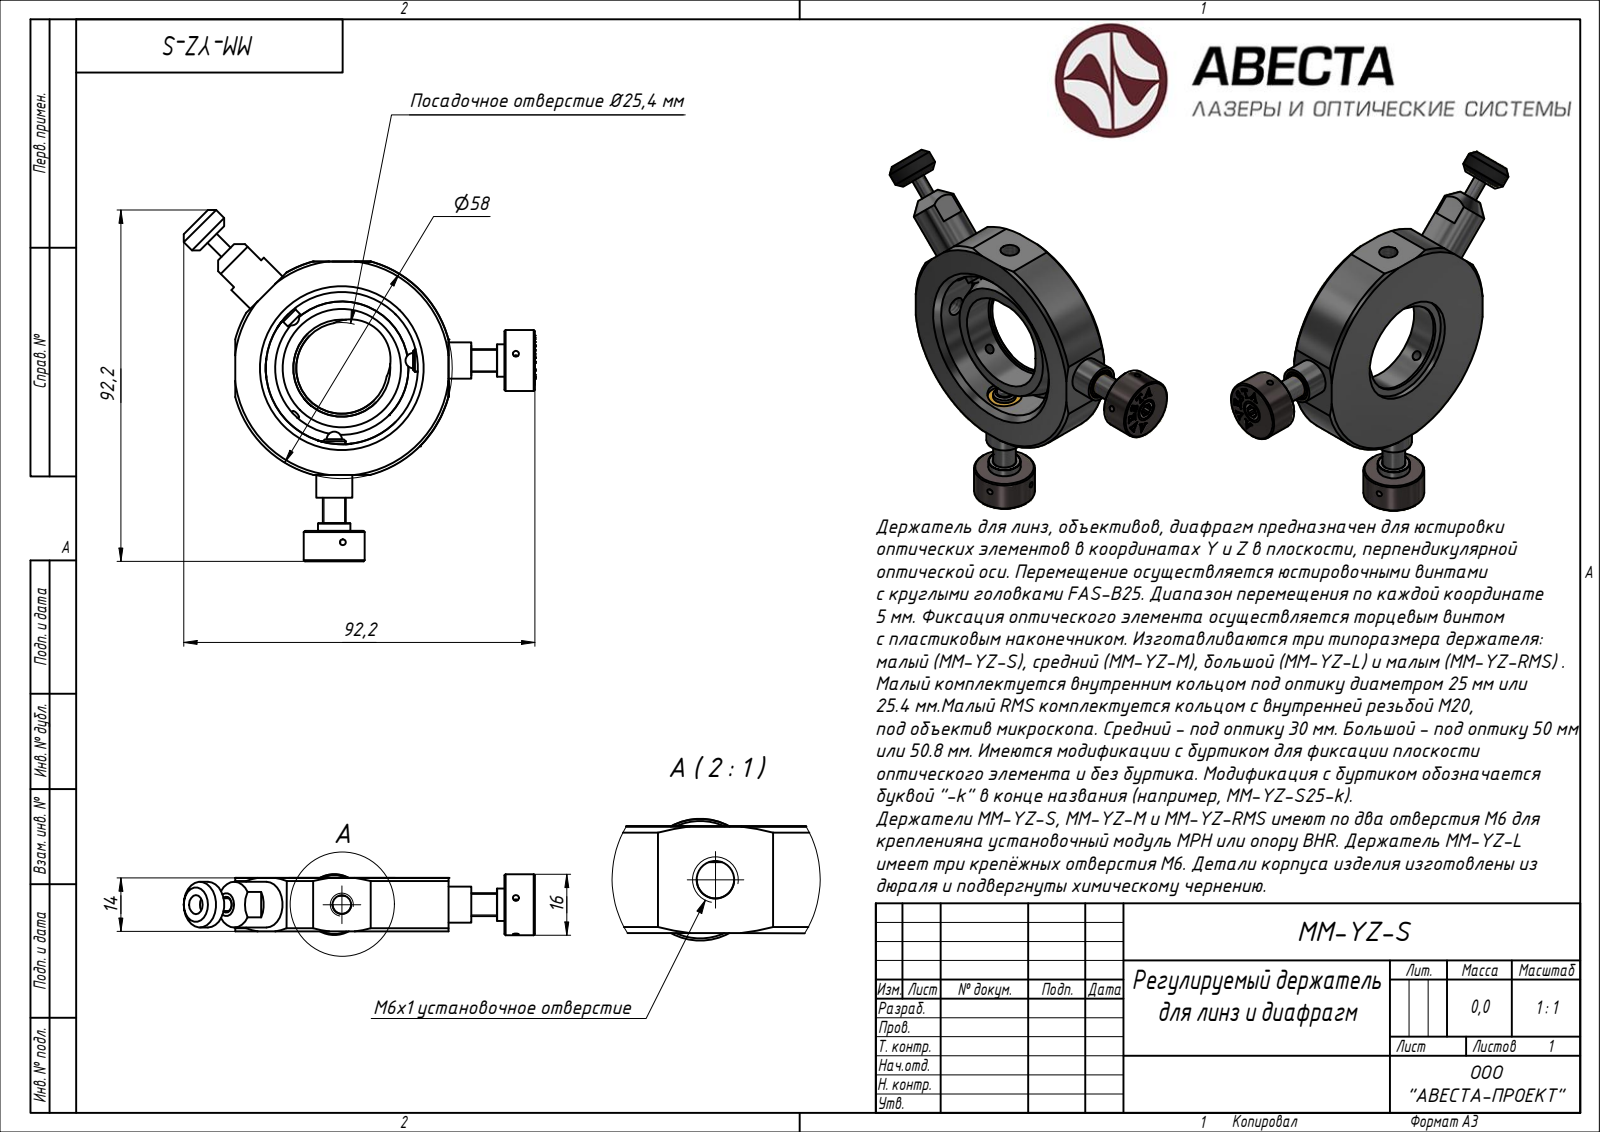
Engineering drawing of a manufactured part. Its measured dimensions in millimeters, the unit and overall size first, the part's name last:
Units: millimetres
Overall size (bounding box): 212.34 × 94.44 × 90.04
Volume: 39 975 mm³ · Surface area: 56 881 mm²
Bodies: 32 solids, 1748 faces (0 planar, 0 cylindrical, 1748 other)
Part name (STEP PRODUCT): MM-YZ-25.4; MM-YZ-25.4_Substitute_1; Block 03; Block 04 (+4 more)
STEP written by: ST-DEVELOPER v15 (AUTOMOTIVE_DESIGN)
